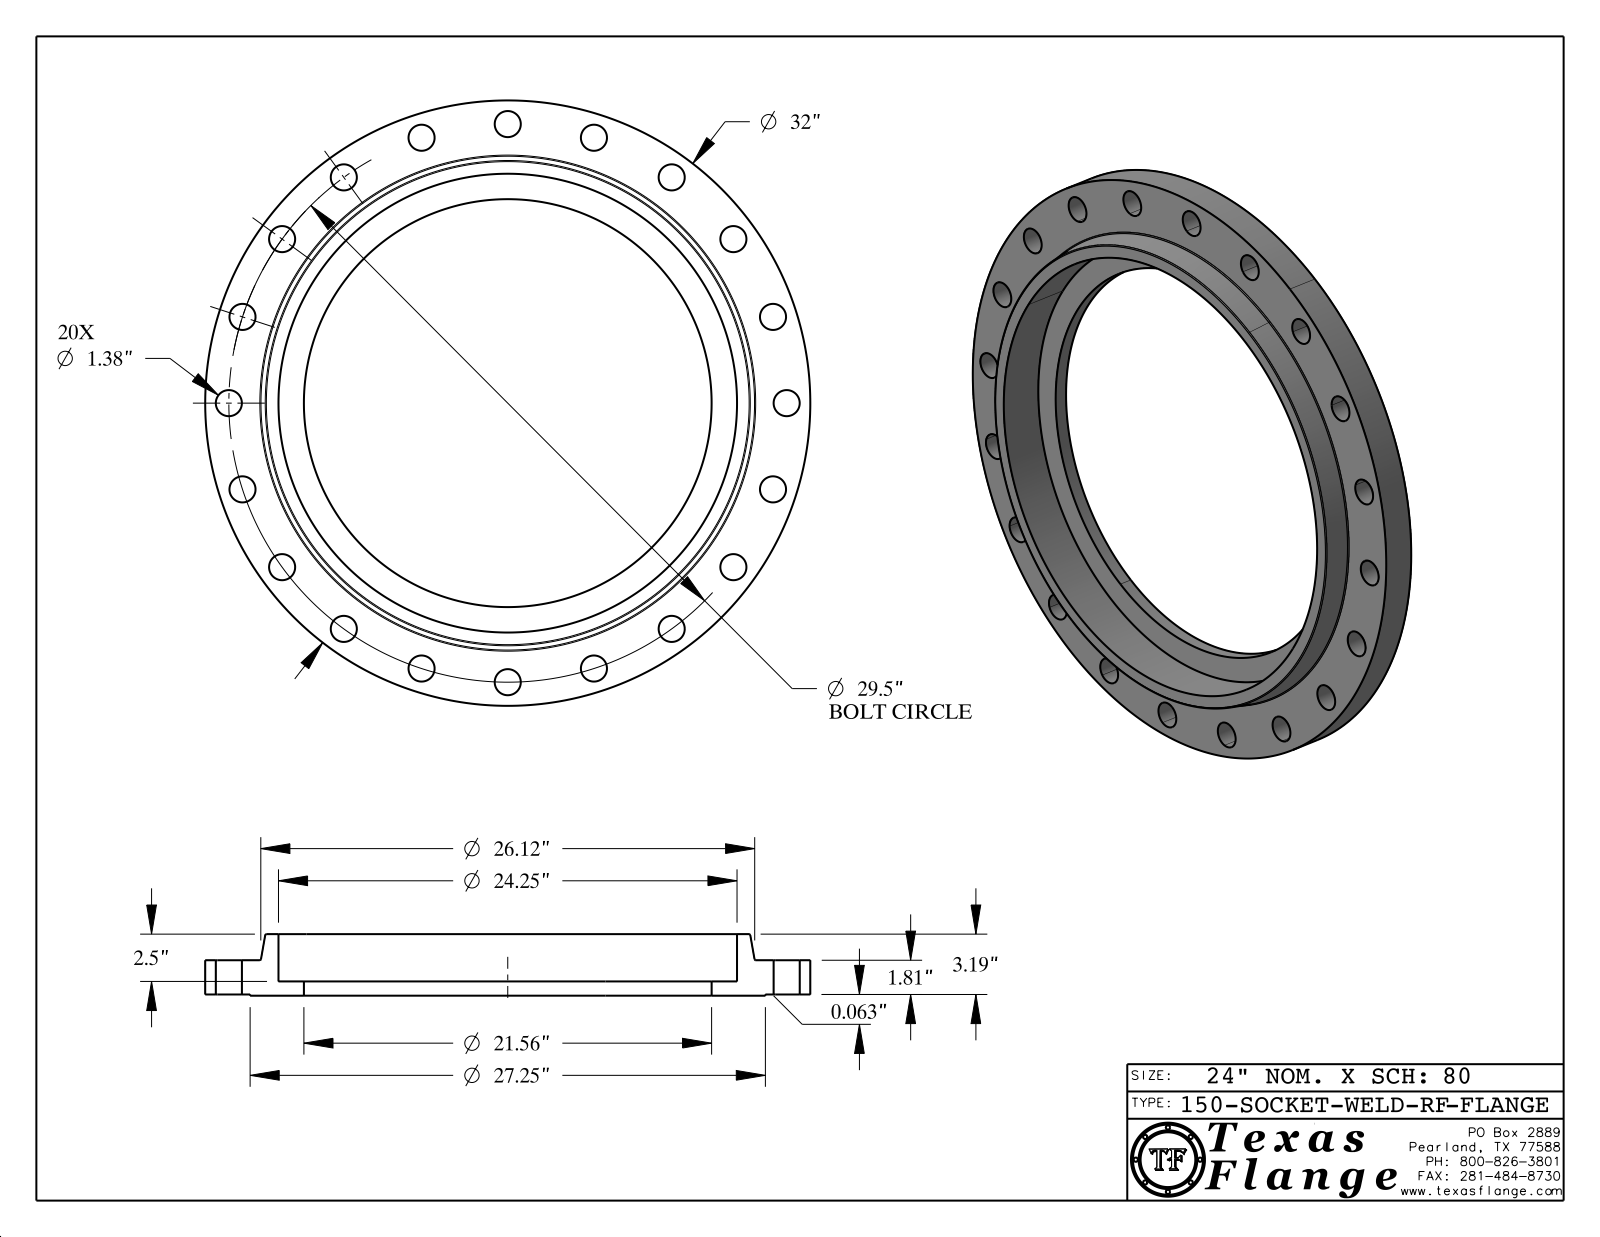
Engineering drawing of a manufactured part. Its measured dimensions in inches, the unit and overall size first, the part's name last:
Units: inches
Overall size (bounding box): 32 × 32 × 3.253
Round holes (diameter × count): ⌀1.38 ×20, ⌀0.495 ×1, ⌀21.562 ×1, ⌀24.25 ×1
Round bosses / shafts (diameter × count): ⌀0.03 ×8, ⌀32 ×1, ⌀27.25 ×1, ⌀0.39 ×1
Main face-to-face distances: 1.872, 0.063, 1.81, 0.753, 0.69, 1.12, 3.253, 3.19, 2.5, 1.38
Hole centre spacings: 14.75, 29.137, 4.615, 17.34, 20.859, 23.866, 26.285, 9.116
Volume: 734.3 in³ · Surface area: 1 496 in²
Bodies: 1 solid, 444 faces (370 planar, 68 cylindrical, 6 other)
Part name (STEP PRODUCT): 150-SOCKET-WELD-RF
STEP written by: CATIA V5 STEP AP214 (AUTOMOTIVE_DESIGN)
